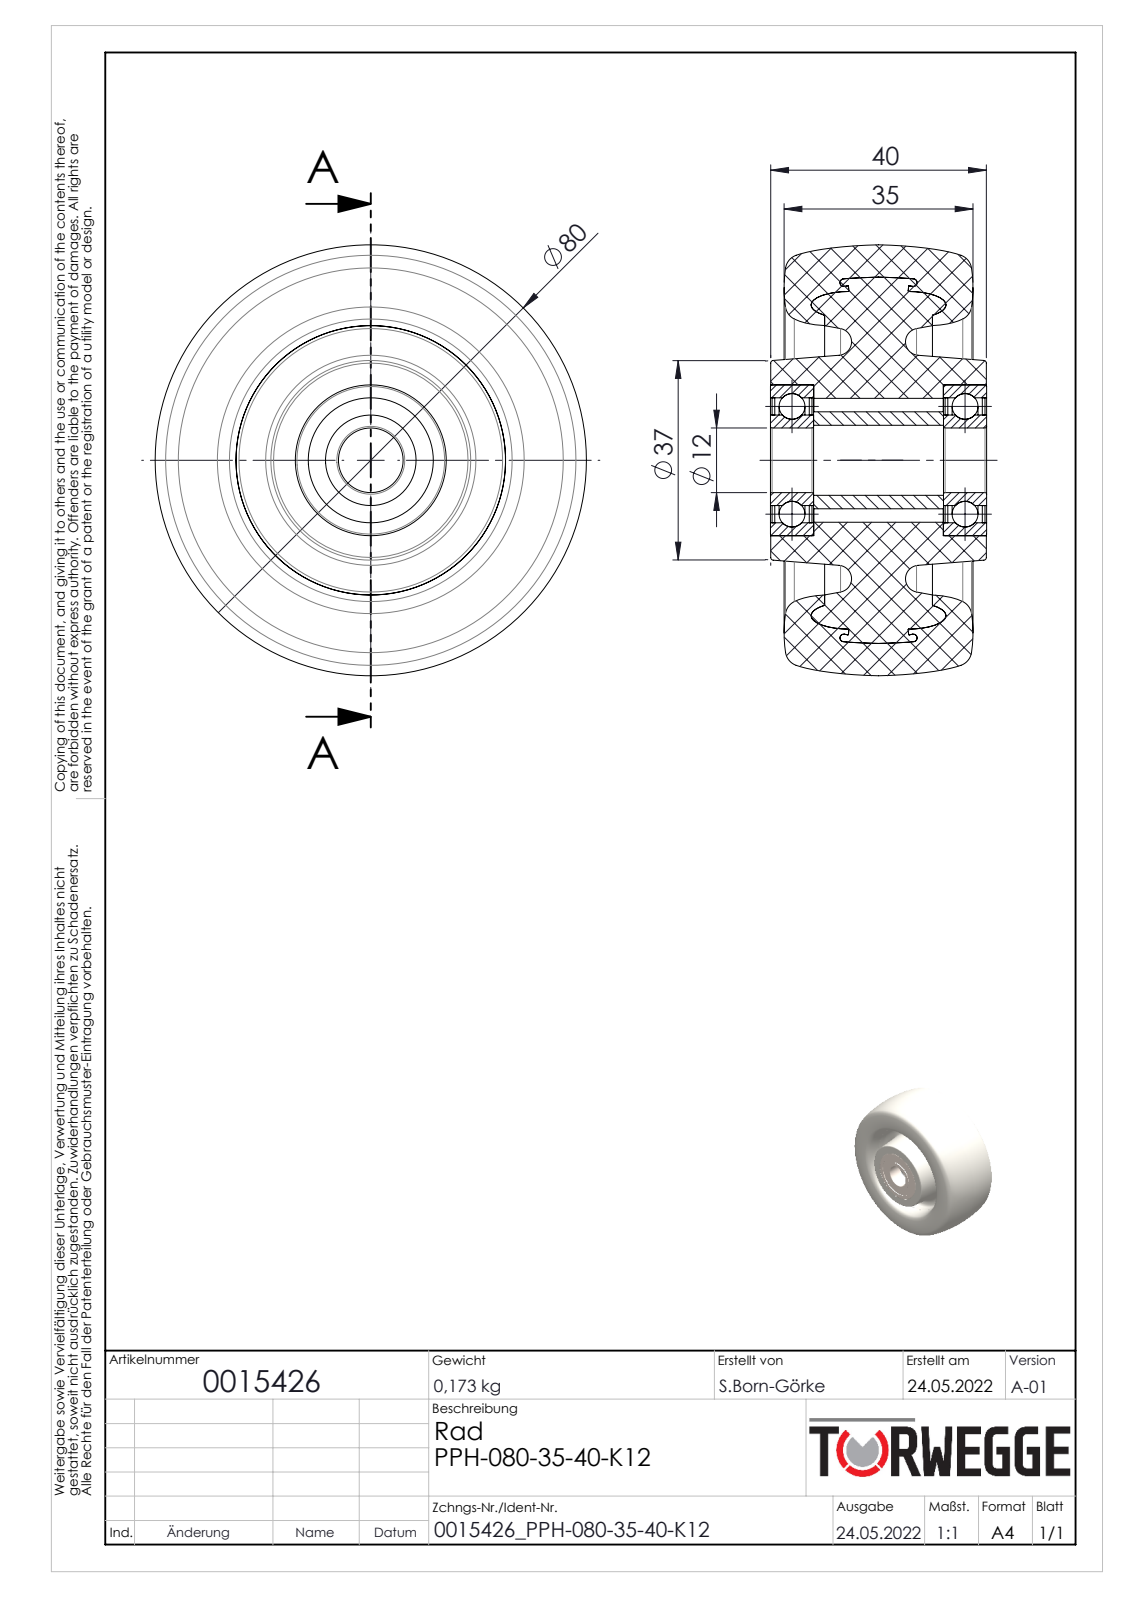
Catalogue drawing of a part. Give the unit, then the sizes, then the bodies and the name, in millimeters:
Units: millimetres
Overall size (bounding box): 80 × 80 × 40.1
Round holes (diameter × count): ⌀12 ×1, ⌀13 ×1, ⌀16.8 ×1, ⌀23 ×1, ⌀23.2 ×1, ⌀28 ×1
Round bosses / shafts (diameter × count): ⌀18 ×1
Partial cylindrical surfaces — rounded edges, fillets, slot ends (radius × count): R31.4 ×1
Main face-to-face distances: 32.1, 32.05, 8, 10, 30, 0.8, 0.5, 7.2, 7.7, 6.9
Volume: 142 537 mm³ · Surface area: 55 384 mm²
Bodies: 13 solids, 386 faces (50 planar, 64 cylindrical, 272 other)
Part name (STEP PRODUCT): 0015426
STEP written by: SolidWorks 2020 (AUTOMOTIVE_DESIGN)
